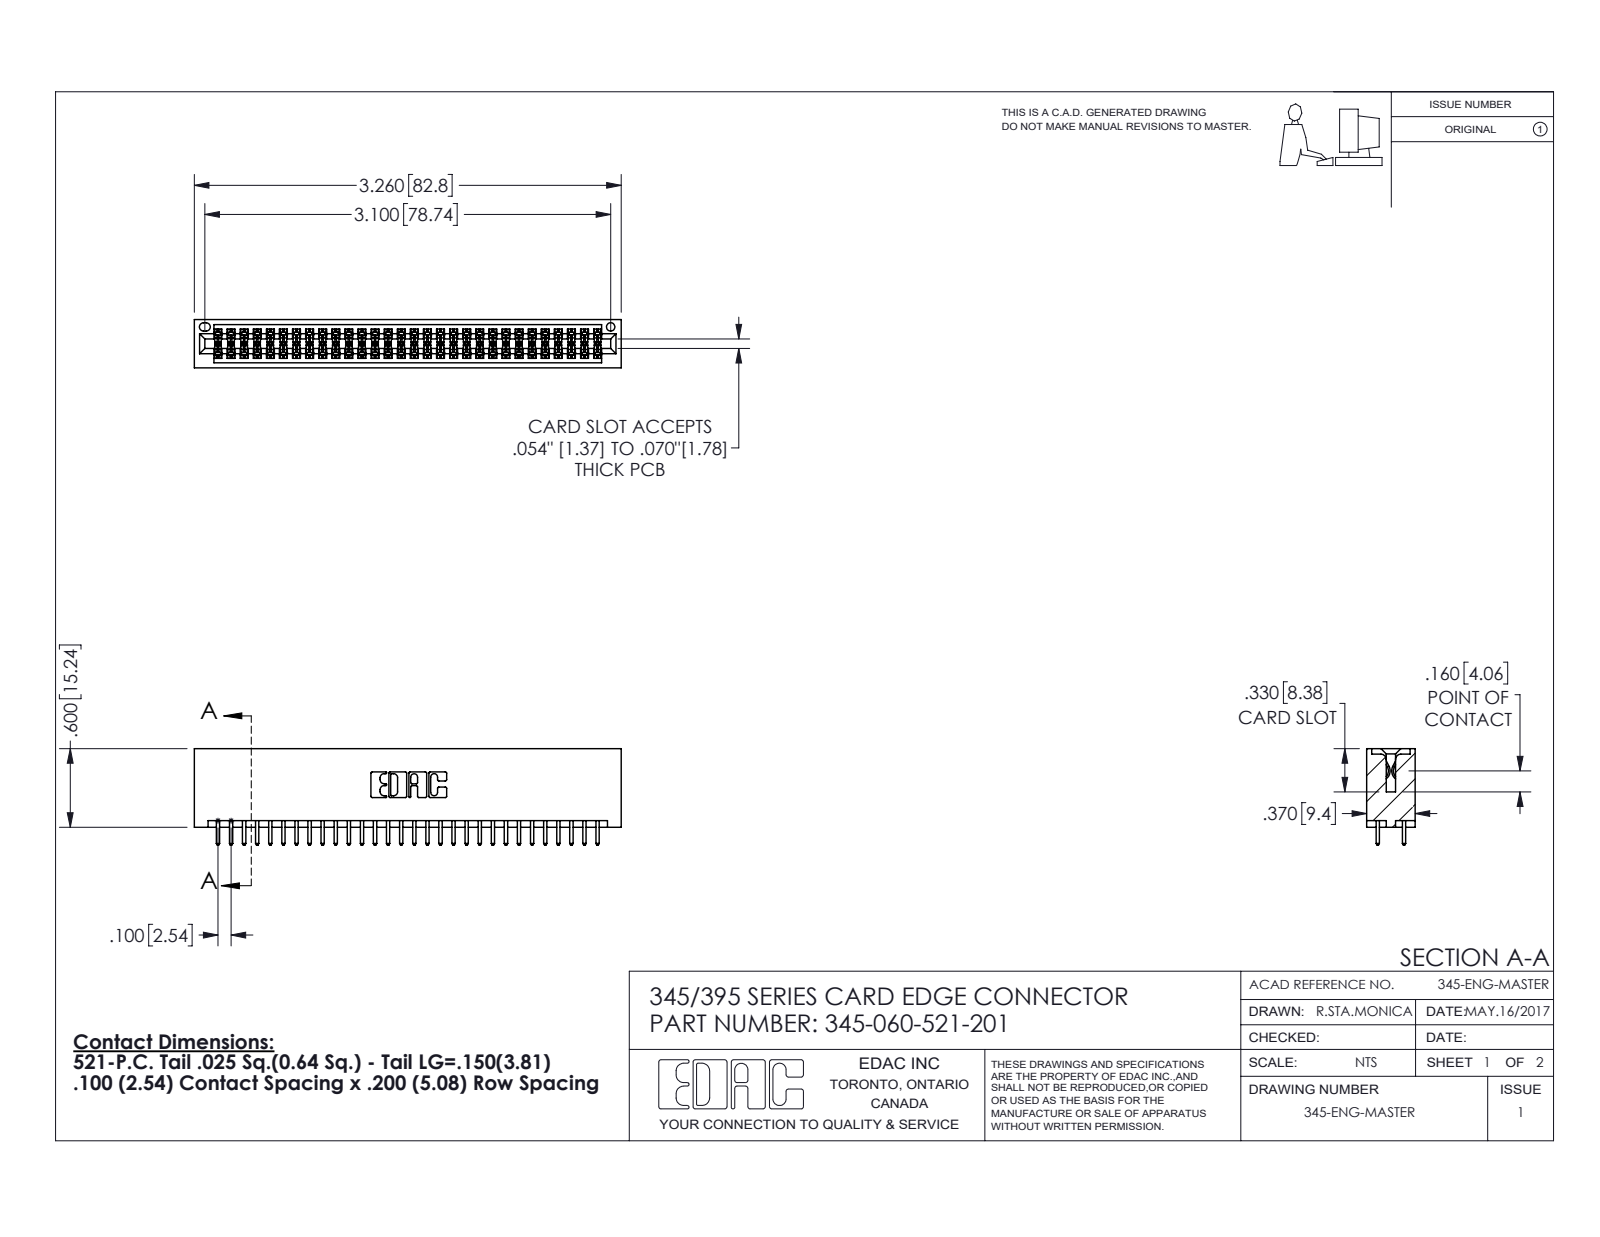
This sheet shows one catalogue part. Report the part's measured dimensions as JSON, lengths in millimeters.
{"part_name": "345 Part_No Mounting Lugs; 345-060-521-201; 345-292-001_345-293-121", "step_written_by": "SolidWorks 2016 (CONFIG_CONTROL_DESIGN)", "units": "millimeters", "bodies": {"solids": 61, "faces": 3118, "planar": 2056, "cylindrical": 1062, "other": 0}, "overall_size": [82.8, 18.7, 9.4], "volume_mm3": 8520, "surface_area_mm2": 12510, "round_holes": [[1.6, 1]], "partial_cylinders_radius": [[0.2, 90], [0.3, 60], [0.3, 22], [0.2, 6], [0.8, 6], [0.7, 3], [0.4, 2], [0.5, 2]], "face_to_face_distances": [7.6, 1.8, 5.1, 2.5, 6.9, 0.6, 9.4, 5.7, 4.4, 3.8]}
